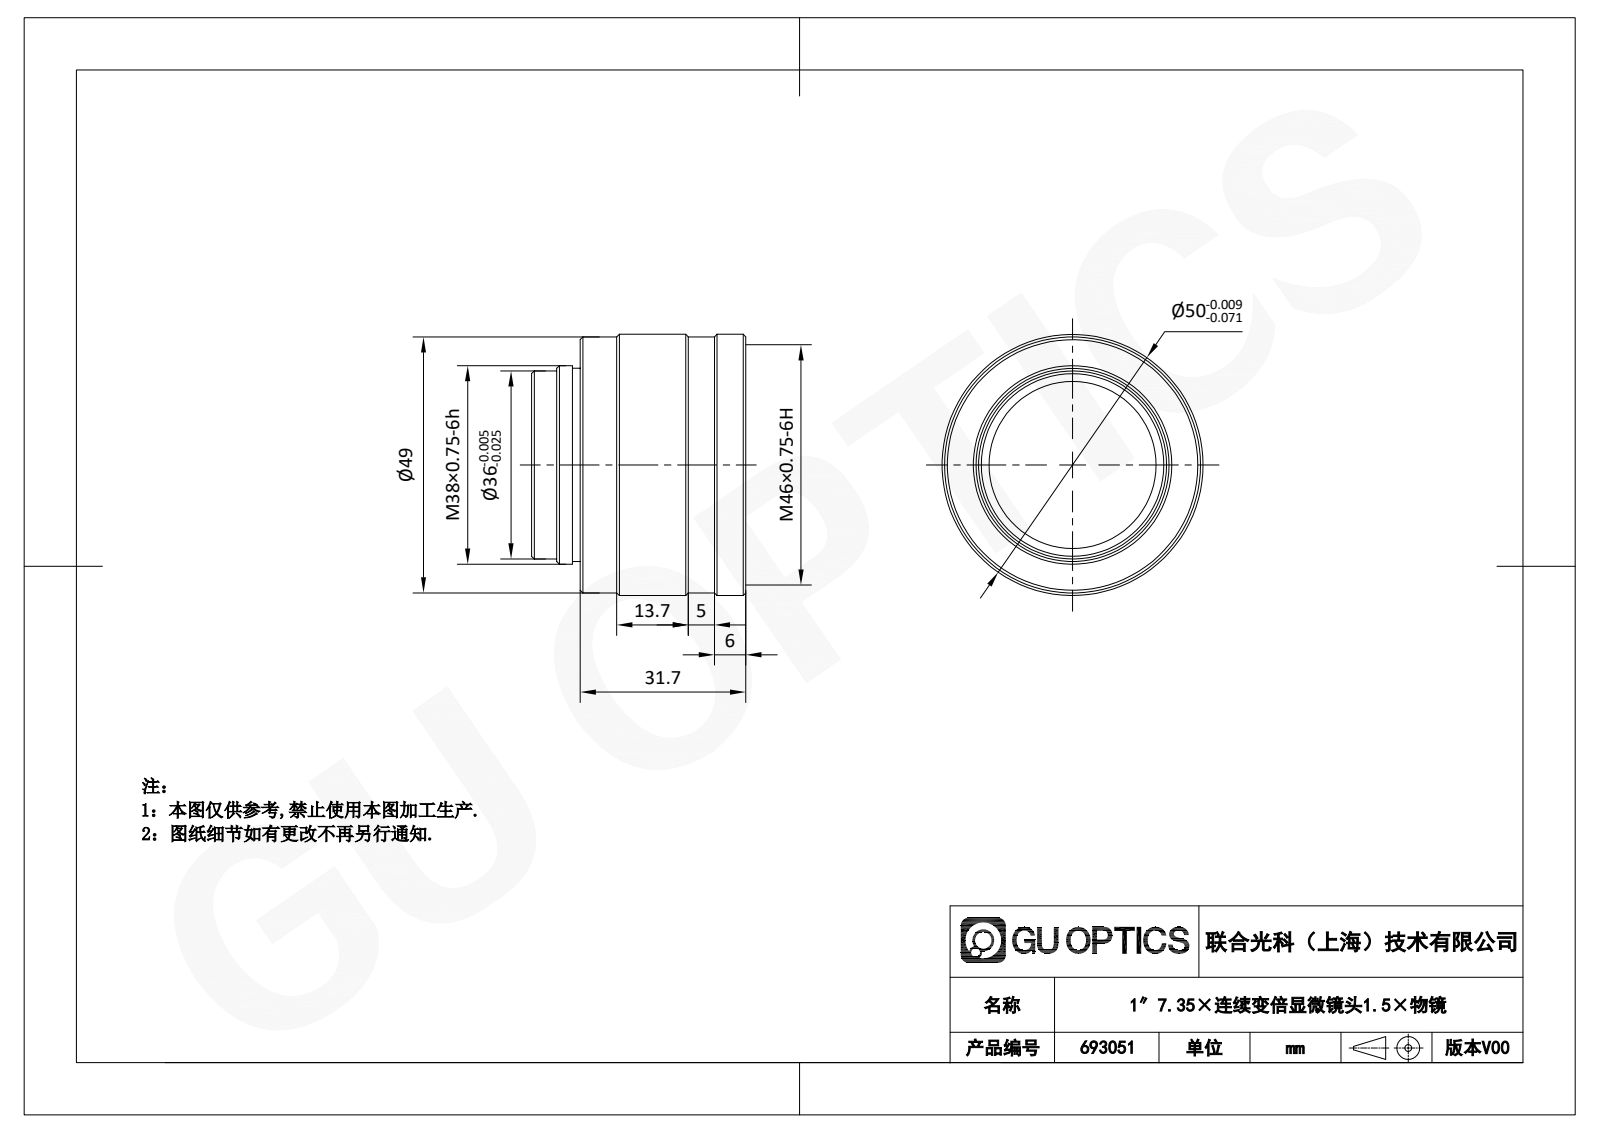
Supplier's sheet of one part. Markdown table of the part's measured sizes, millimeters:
| quantity | value |
| --- | --- |
| part name | 693051T |
| STEP written by | SolidWorks 2020 (CONFIG_CONTROL_DESIGN) |
| units | millimeters |
| bodies | 1 solid, 23 faces (5 planar, 9 cylindrical, 9 other) |
| overall size | 50 × 50 × 41 |
| volume | 66 354 mm³ |
| surface area | 10 577 mm² |
| round holes (diameter × count) | 32 × 1, 46 × 1 |
| round bosses / shafts (diameter × count) | 50 × 1, 49 × 1, 38 × 1, 37 × 1, 36 × 1 |
| main face-to-face distances | 31.7, 41, 9.3, 33.2, 1.5, 7.8, 36.2, 4.5, 3, 4.8 |
